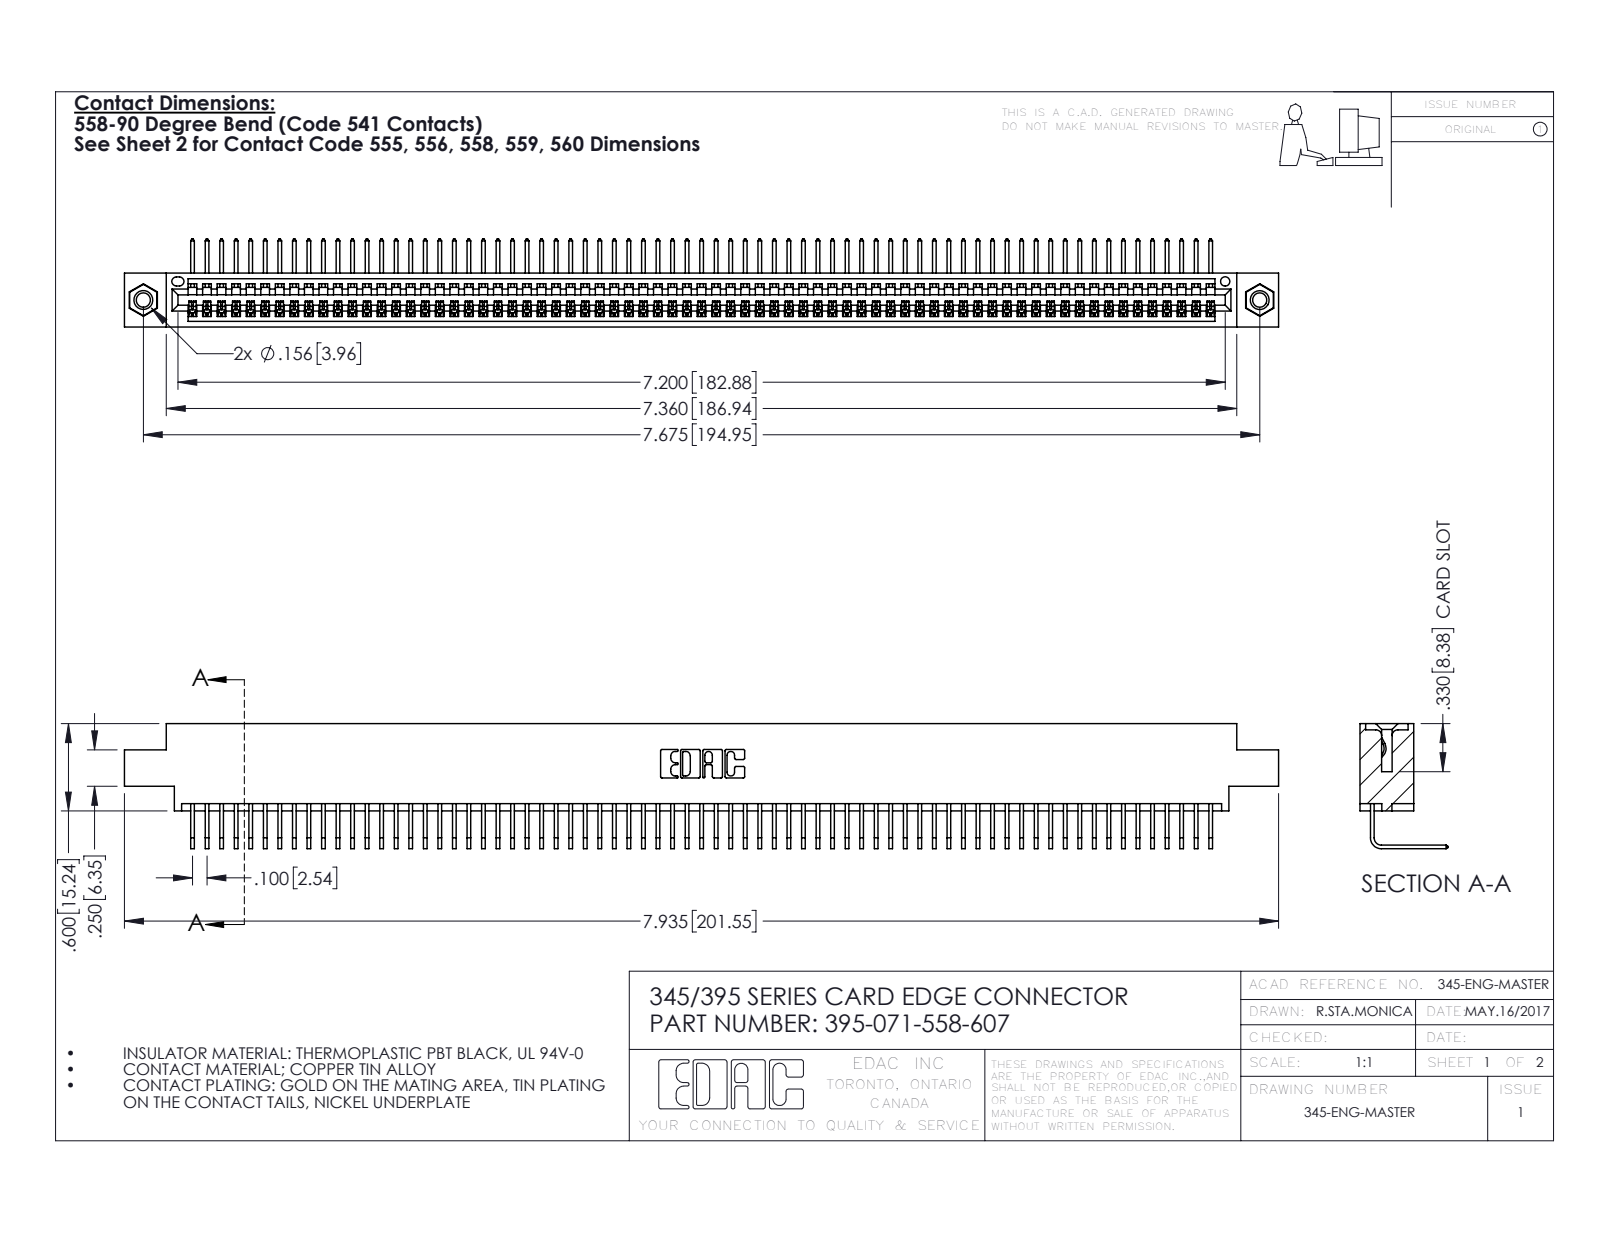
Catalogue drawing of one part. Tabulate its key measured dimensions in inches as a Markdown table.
| quantity | value |
| --- | --- |
| part name | 345-250-001_345-250-005-103; 345 Part_0.170 Offset - 0.156 Dia-TI; 395-071-558-607; 345-292-001_558 Tail - 2 |
| STEP written by | SolidWorks 2016 (CONFIG_CONTROL_DESIGN) |
| units | inches |
| bodies | 74 solids, 4450 faces (3098 planar, 1336 cylindrical, 16 other) |
| overall size | 7.935 × 0.859 × 0.605 |
| volume | 1.189 in³ |
| surface area | 43.16 in² |
| round holes (diameter × count) | 0.098 × 2, 0.125 × 2, 0.156 × 2, 0.064 × 1 |
| round bosses / shafts (diameter × count) | 0.155 × 2 |
| partial cylindrical surfaces (radius × count) | 0.006 × 142, 0.01 × 22, 0.007 × 6, 0.031 × 6, 0.026 × 3, 0.031 × 2, 0.04 × 2, 0.014 × 1 |
| main face-to-face distances | 0.072, 0.298, 0.37, 0.2, 0.098, 0.272, 0.025, 0.225, 0.175, 0.149 |
| hole center spacings | 0.27, 7.439, 7.675 |
